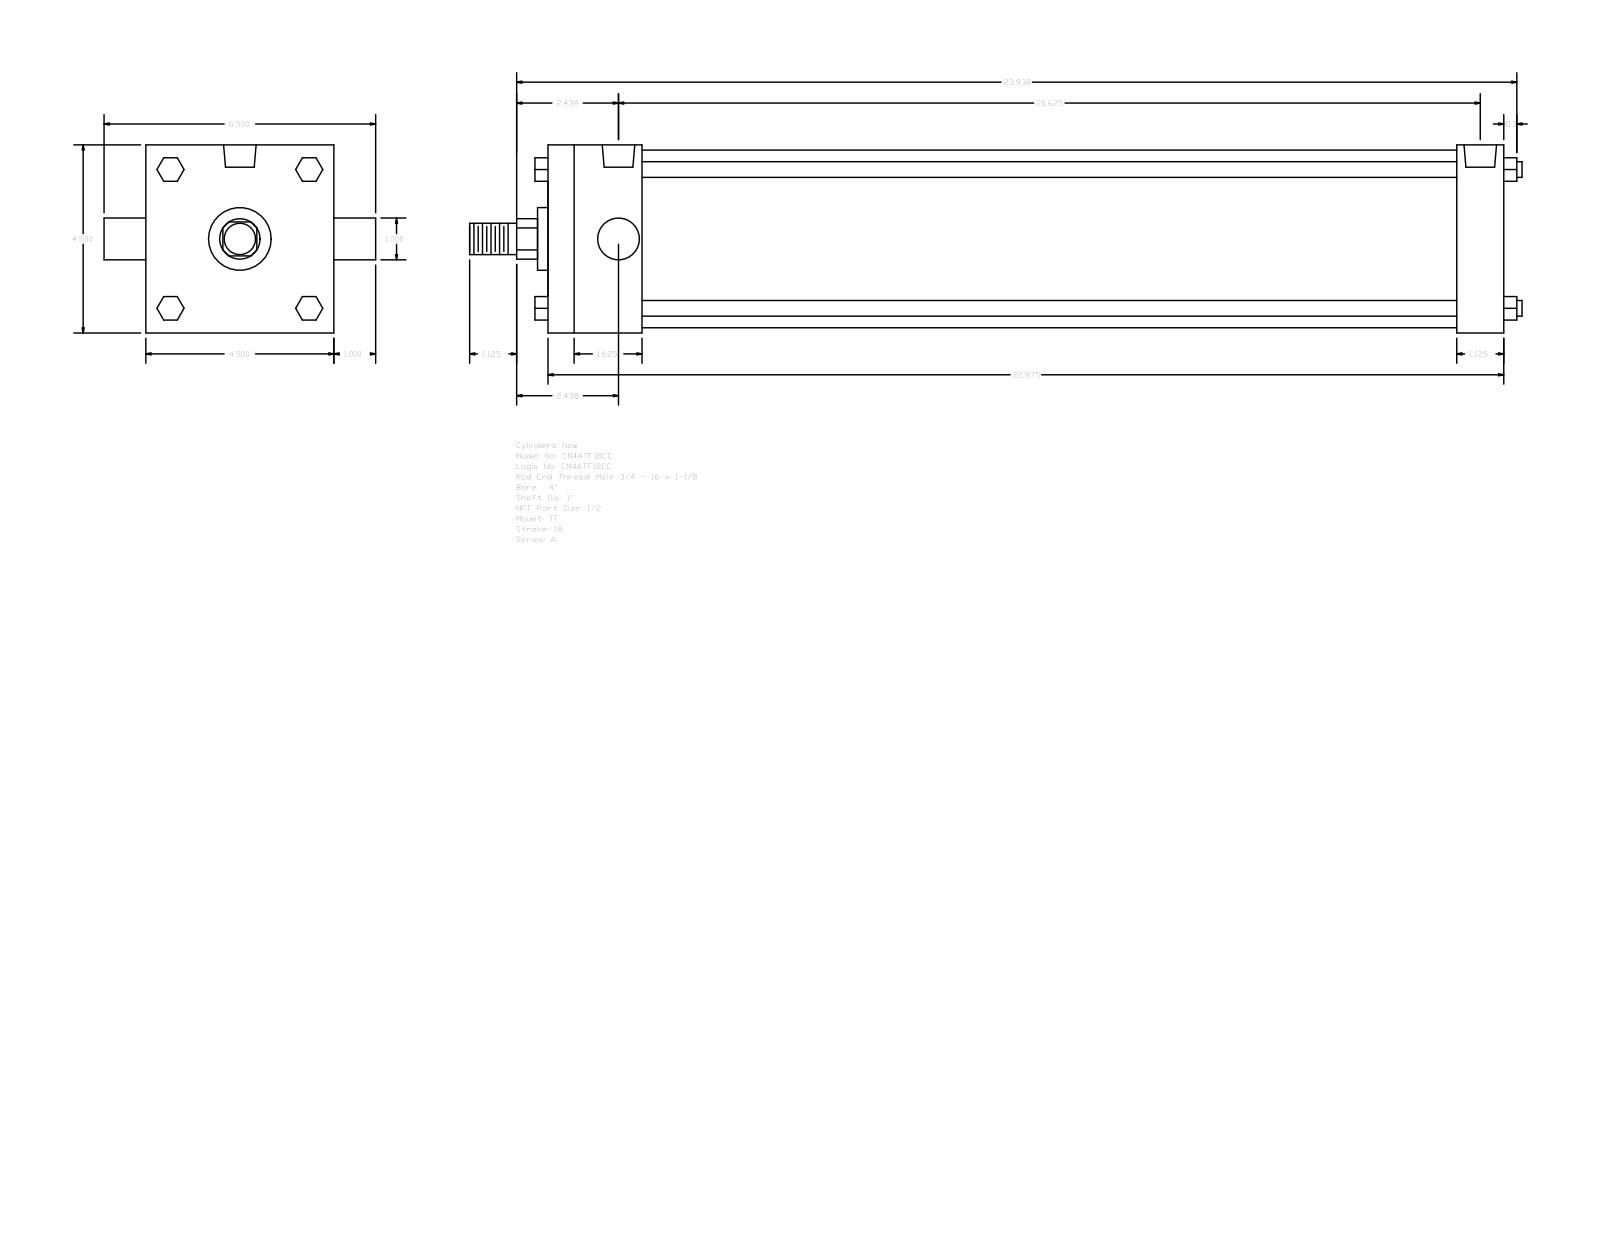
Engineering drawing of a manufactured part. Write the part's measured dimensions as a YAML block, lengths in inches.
part_name: "A_TF__0400_1"
step_written_by: "GSSL Pune (CONFIG_CONTROL_DESIGN)"
units: inches
bodies: {solids: 0, faces: 120, planar: 92, cylindrical: 28, other: 0}
overall_size: [25.187, 6.5, 4.5]
round_holes:
  - {diameter: 0.344, count: 3}
  - {diameter: 0.778, count: 2}
round_bosses_or_shafts:
  - {diameter: 0.375, count: 4}
  - {diameter: 1, count: 2}
  - {diameter: 4.25, count: 1}
  - {diameter: 1.5, count: 1}
  - {diameter: 0.75, count: 1}
partial_cylinders:
  - {radius: 0.484, count: 1}
face_to_face_distances: [4.5, 22.875, 21.75, 1.125, 2.25, 19.5, 20.625, 0.563, 1.66, 2.875]
hole_center_spacings: [0.125, 20.5, 20.375, 20.625]
